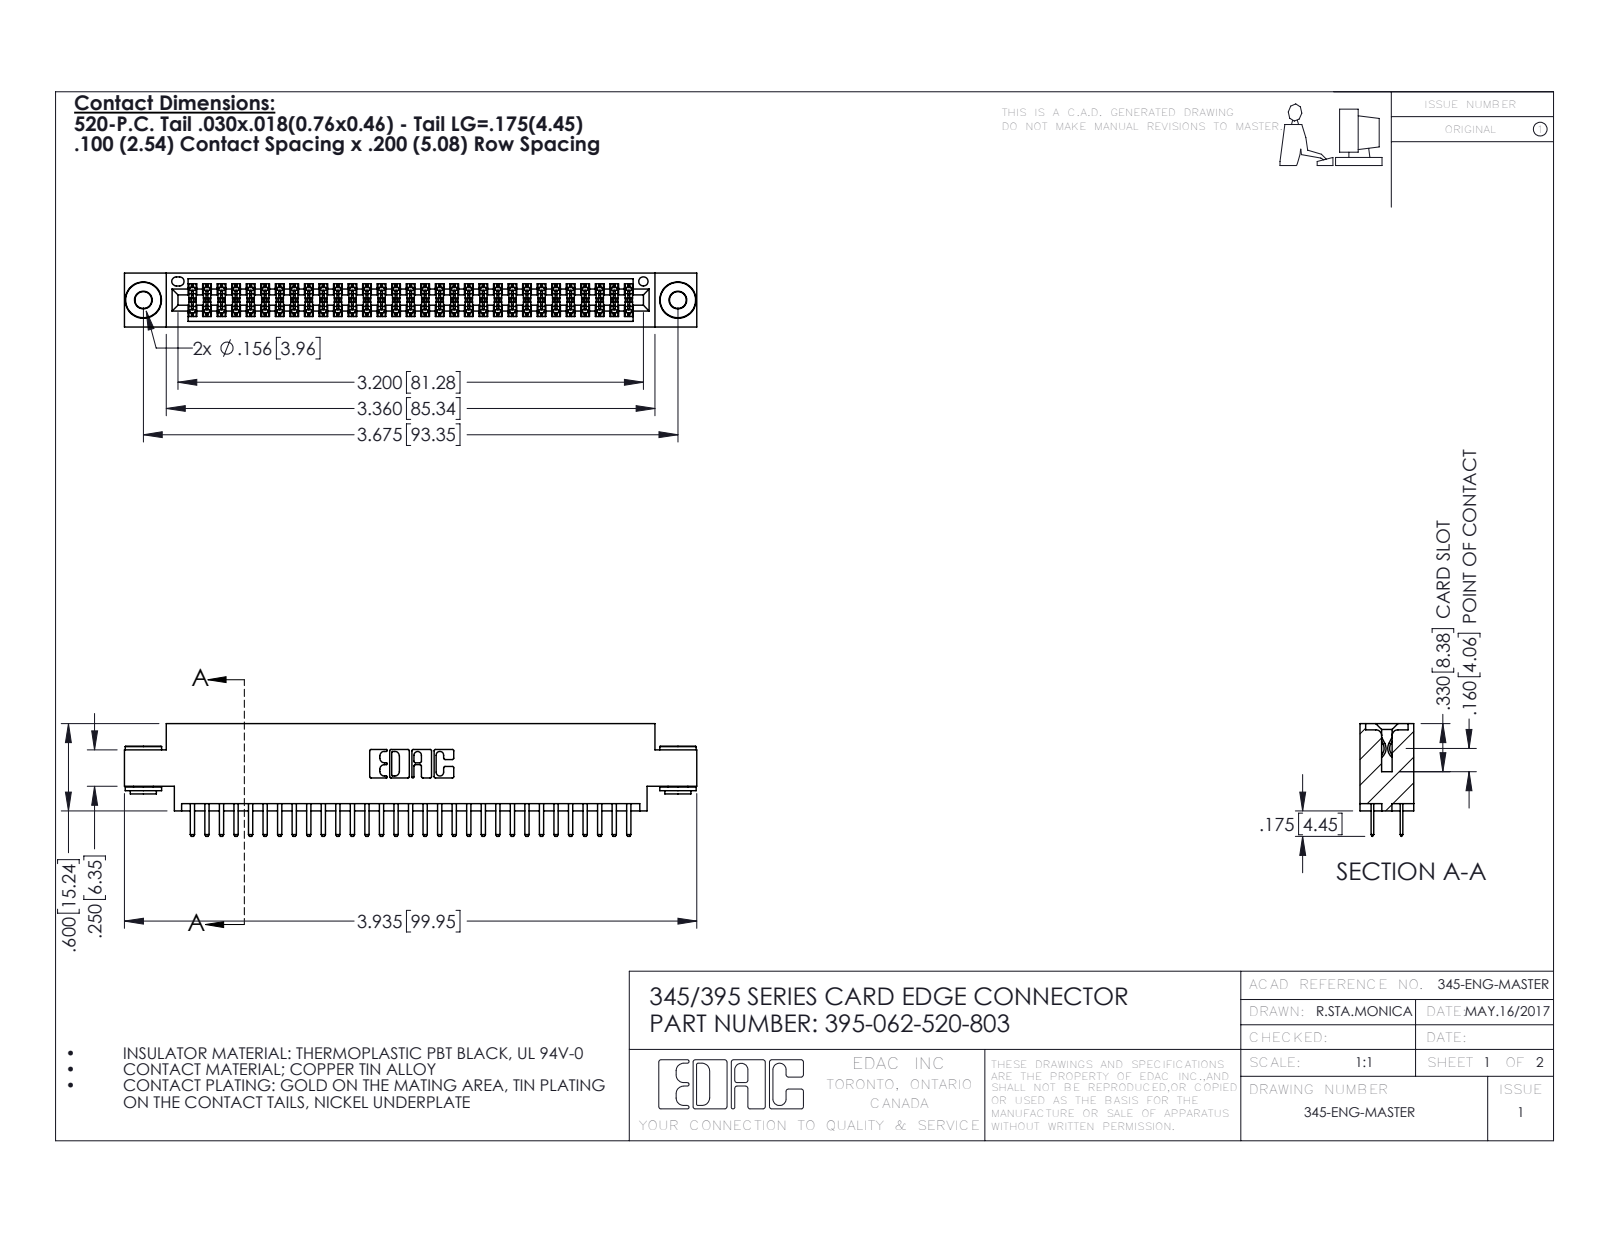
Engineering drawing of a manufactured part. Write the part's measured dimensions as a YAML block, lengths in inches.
part_name: "345-250-002_345-250-002-102; 345-292-001_345-293-120; 345 Part_0.170 Offset - 0.156 Dia-TH; 395-062-520-803"
step_written_by: "SolidWorks 2016 (CONFIG_CONTROL_DESIGN)"
units: inches
bodies: {solids: 65, faces: 3516, planar: 2264, cylindrical: 1244, other: 8}
overall_size: [3.935, 0.775, 0.37]
volume: 0.579
surface_area: 21.85
round_holes:
  - {diameter: 0.116, count: 2}
  - {diameter: 0.156, count: 2}
  - {diameter: 0.064, count: 1}
round_bosses_or_shafts:
  - {diameter: 0.25, count: 2}
  - {diameter: 0.18, count: 2}
  - {diameter: 0.136, count: 2}
partial_cylinders:
  - {radius: 0.006, count: 93}
  - {radius: 0.01, count: 66}
  - {radius: 0.01, count: 22}
  - {radius: 0.007, count: 6}
  - {radius: 0.031, count: 6}
  - {radius: 0.026, count: 3}
  - {radius: 0.014, count: 2}
  - {radius: 0.019, count: 2}
face_to_face_distances: [0.072, 0.298, 0.2, 0.37, 0.098, 0.272, 0.025, 0.225, 0.175, 0.022]
hole_center_spacings: [0.27, 3.44, 3.675]
